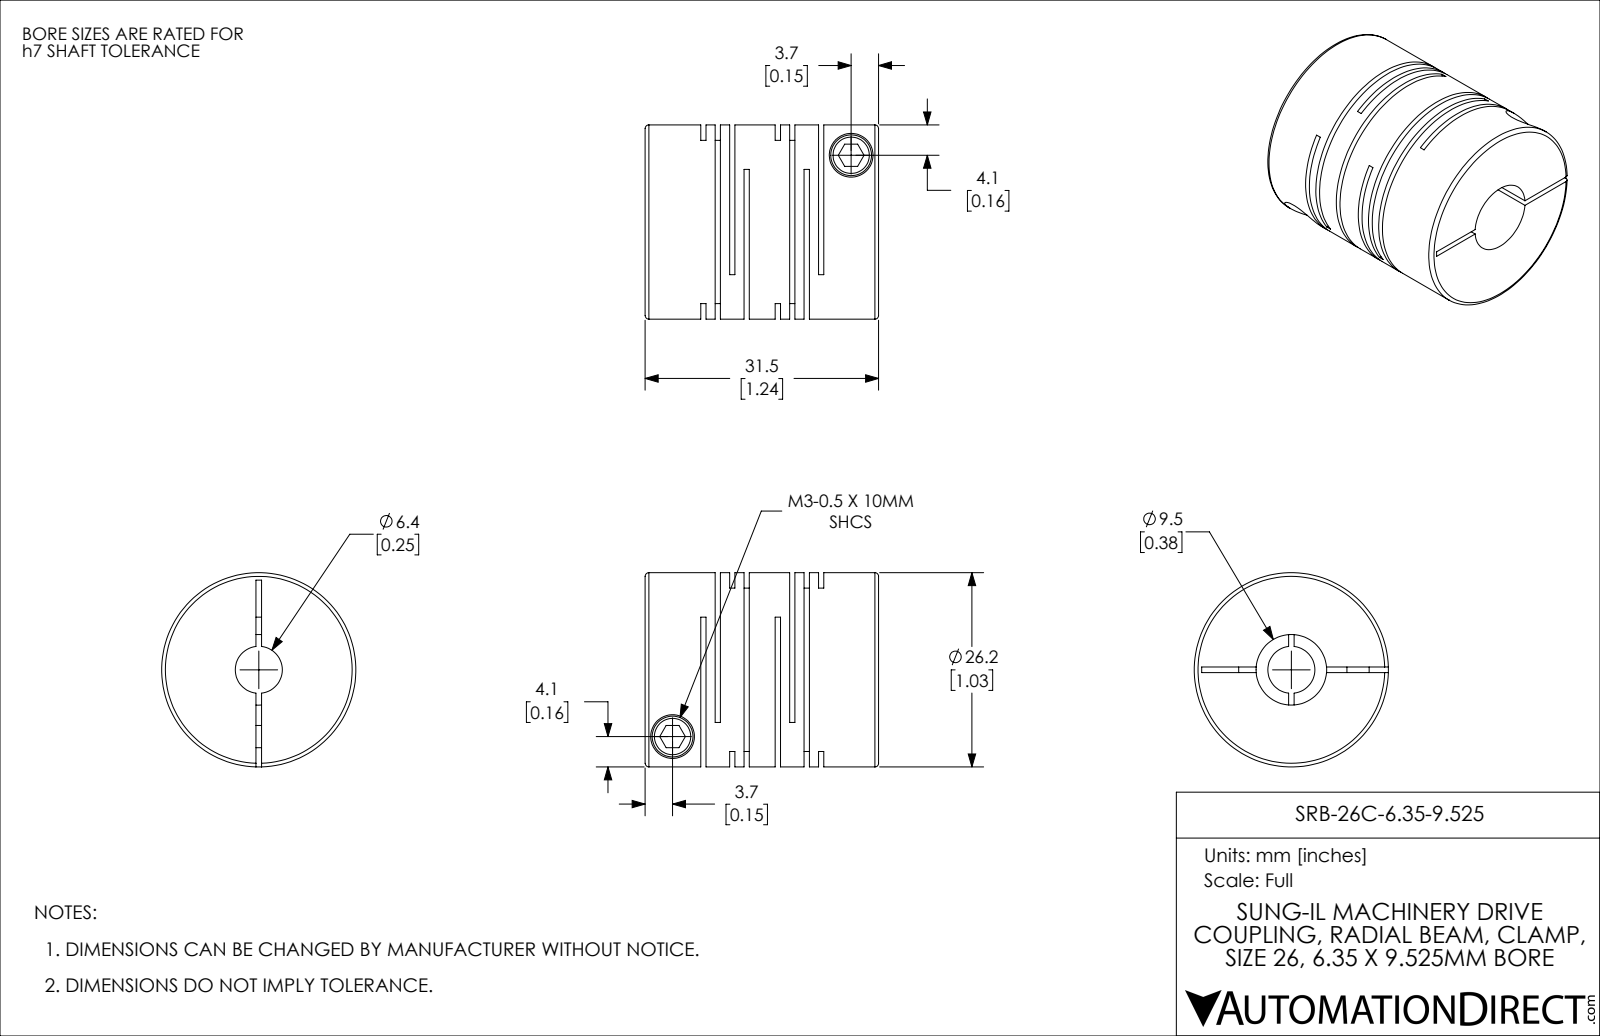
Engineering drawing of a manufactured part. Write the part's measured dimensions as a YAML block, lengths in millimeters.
part_name: "SRB-26C-6.35-9.525"
step_written_by: "SolidWorks 2021 (CONFIG_CONTROL_DESIGN)"
units: millimeters
bodies: {solids: 1, faces: 114, planar: 60, cylindrical: 42, other: 12}
overall_size: [31.5, 26.2, 26.2]
volume: 12405
surface_area: 10878
round_holes:
  - {diameter: 3, count: 2}
  - {diameter: 5.9, count: 2}
  - {diameter: 6.35, count: 1}
  - {diameter: 9.53, count: 1}
round_bosses_or_shafts:
  - {diameter: 5.5, count: 2}
  - {diameter: 26.2, count: 1}
face_to_face_distances: [1.95, 10.05, 0.71, 3.9, 8.1, 12, 1.24, 2.66, 9.34, 13.95]
